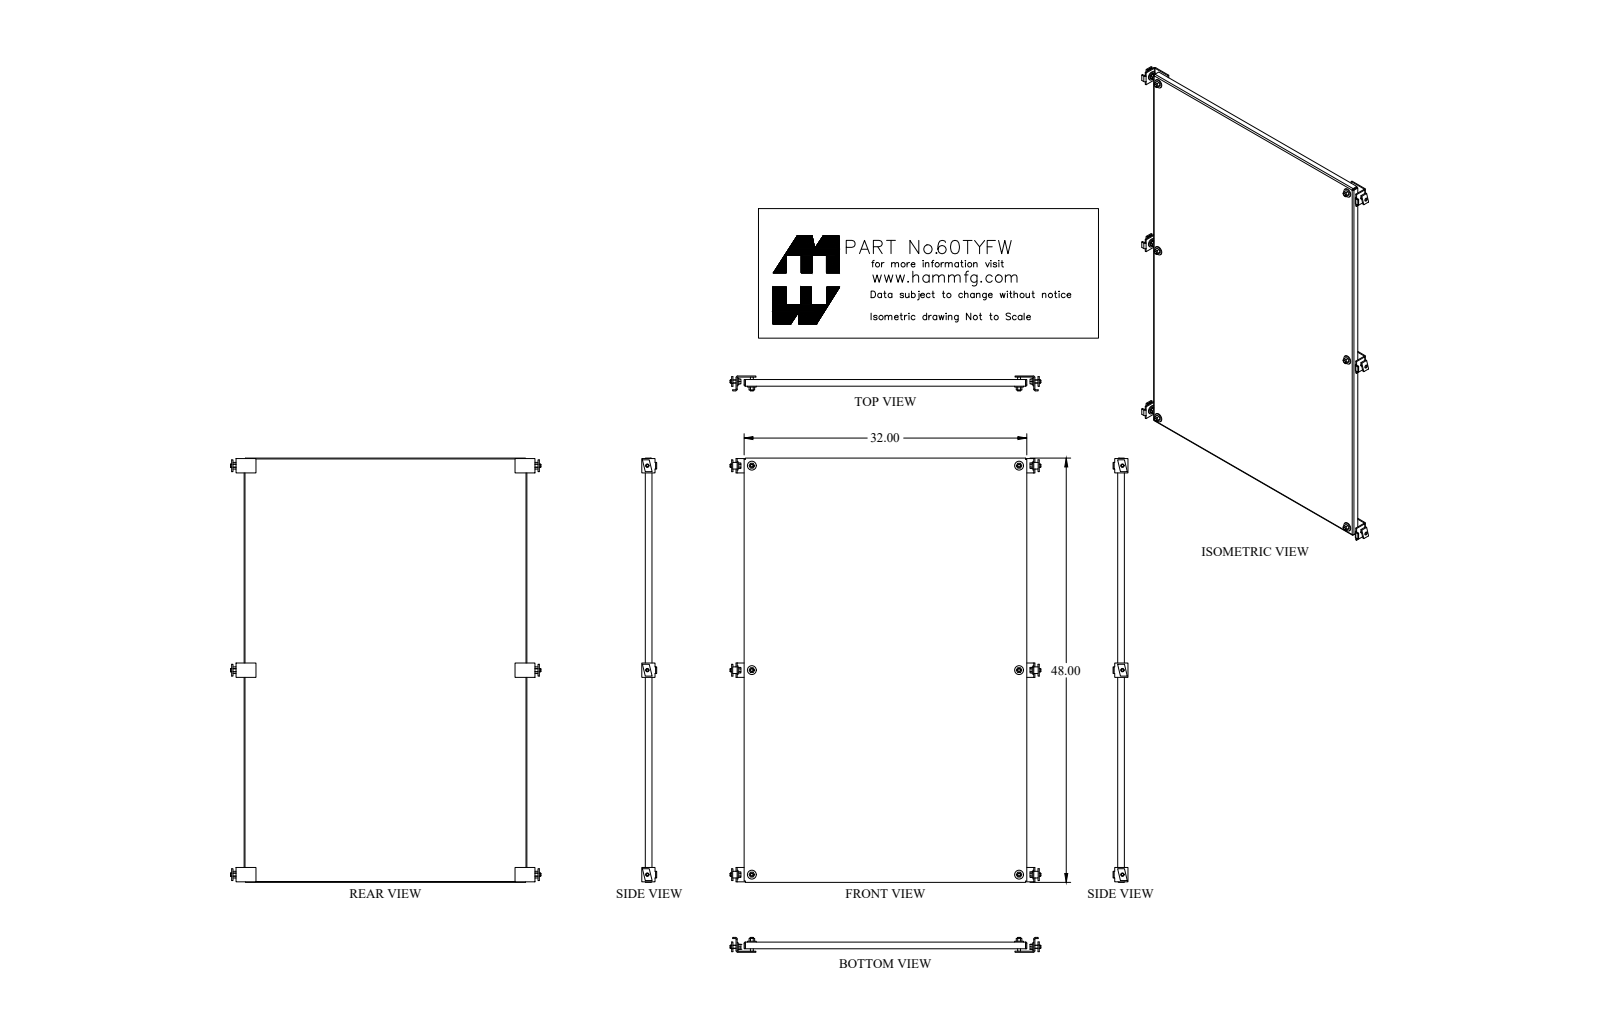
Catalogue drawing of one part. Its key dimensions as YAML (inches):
part_name: "60TYFW_Default"
step_written_by: "SolidWorks 2018 (CONFIG_CONTROL_DESIGN)"
units: inches
bodies: {solids: 1, faces: 42, planar: 22, cylindrical: 20, other: 0}
overall_size: [48, 32, 0.75]
volume: 155
surface_area: 3281
round_holes:
  - {diameter: 0.563, count: 6}
partial_cylinders:
  - {radius: 0.048, count: 4}
  - {radius: 0.143, count: 4}
face_to_face_distances: [0.095, 31.905, 47.905, 31.81, 32, 48, 47.81, 0.75, 0.655, 0.143]
hole_center_spacings: [23.125, 38.077, 30.25, 46.25, 55.265]
